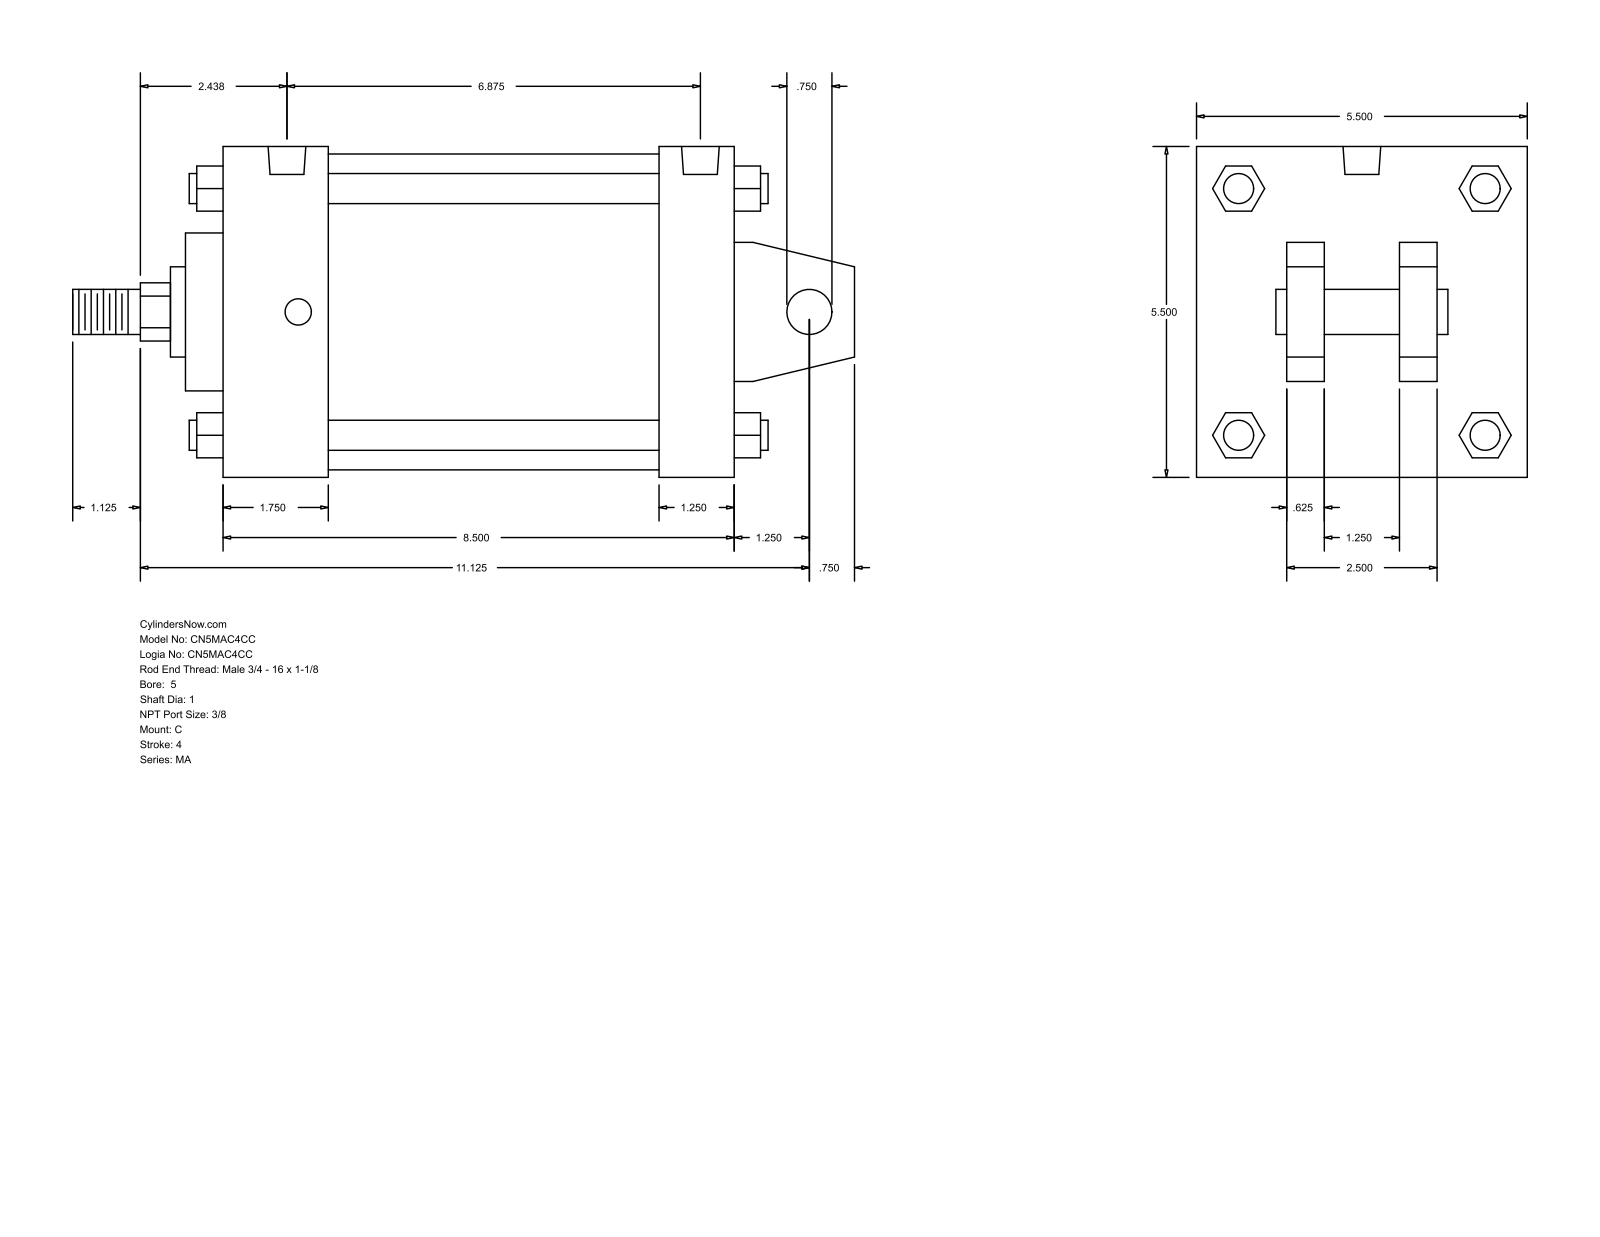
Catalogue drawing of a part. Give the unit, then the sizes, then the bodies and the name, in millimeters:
Units: millimetres
Overall size (bounding box): 330.2 × 139.7 × 139.7
Round holes (diameter × count): ⌀11.11 ×4, ⌀15.93 ×2
Round bosses / shafts (diameter × count): ⌀12.7 ×4, ⌀19.05 ×2, ⌀133.35 ×1, ⌀66.67 ×1, ⌀38.1 ×1, ⌀25.4 ×1
Partial cylindrical surfaces — rounded edges, fillets, slot ends (radius × count): R12.29 ×1
Main face-to-face distances: 139.7, 215.9, 15.87, 184.15, 31.75, 44.46, 139.69, 171.44, 38.1, 101.6
Hole centre spacings: 4.76, 165.11, 169.87, 174.63
Bodies: 0 solids, 141 faces (109 planar, 32 cylindrical, 0 other)
Part name (STEP PRODUCT): MA_C__0500_1
STEP written by: GSSL Pune (CONFIG_CONTROL_DESIGN)
